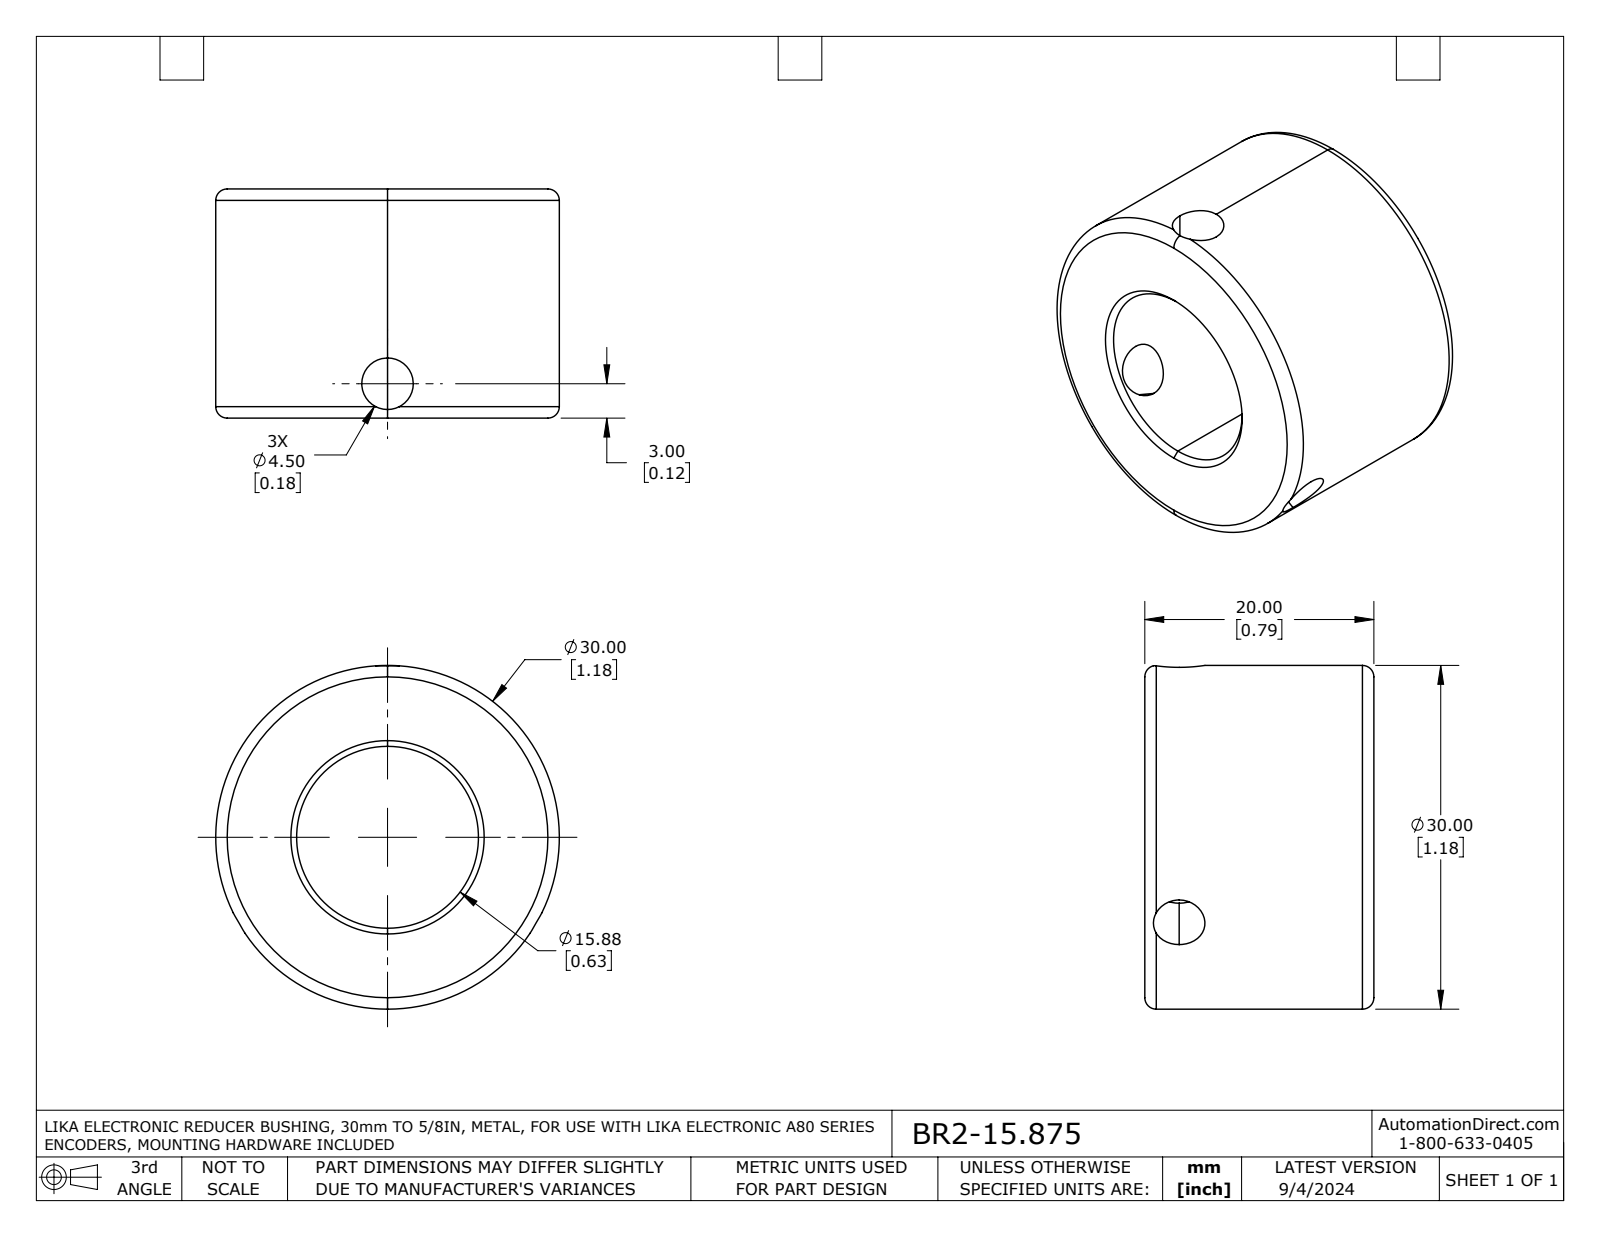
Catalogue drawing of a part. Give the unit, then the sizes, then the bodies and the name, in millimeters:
Units: millimetres
Overall size (bounding box): 30 × 30 × 20
Round holes (diameter × count): ⌀4.5 ×3, ⌀15.9 ×1
Round bosses / shafts (diameter × count): ⌀30 ×1
Main face-to-face distances: 20
Volume: 9 780 mm³ · Surface area: 3 996 mm²
Bodies: 1 solid, 25 faces (2 planar, 13 cylindrical, 10 other)
Part name (STEP PRODUCT): BR2-15.875
STEP written by: SolidWorks 2021 (AUTOMOTIVE_DESIGN)
